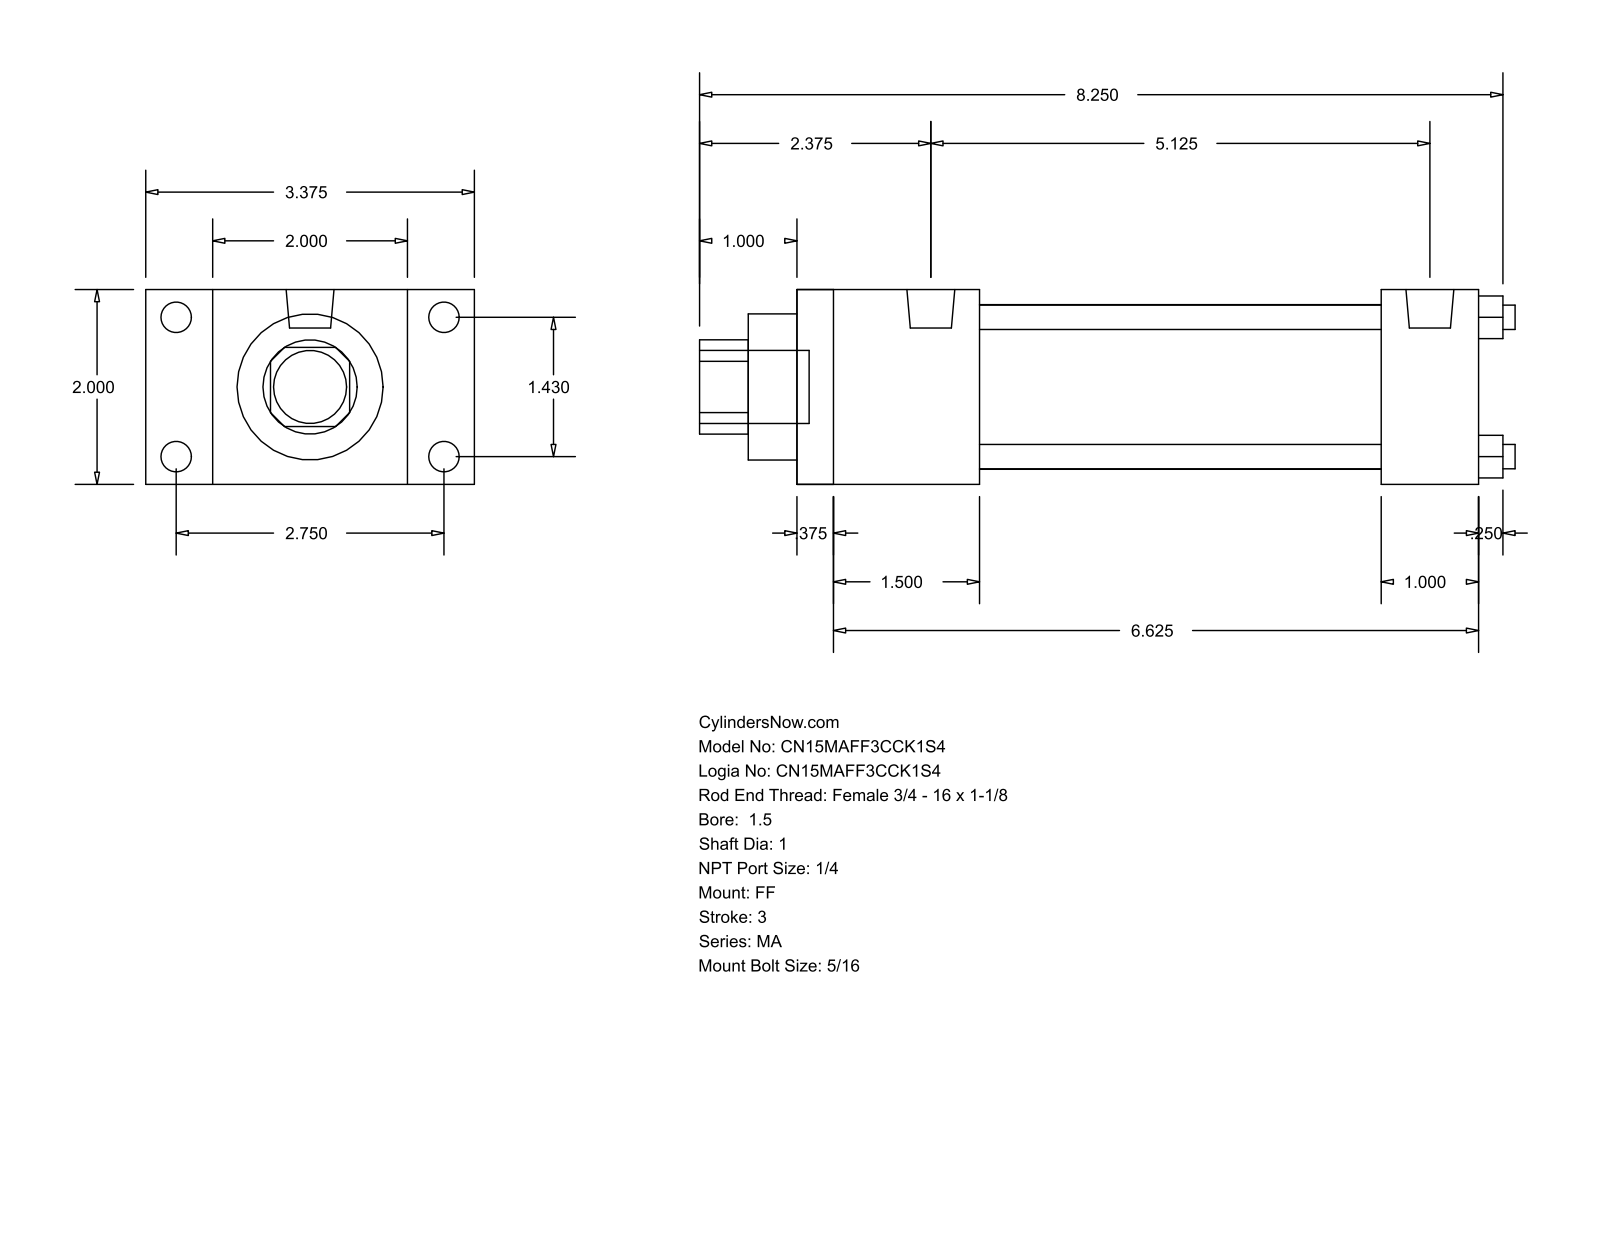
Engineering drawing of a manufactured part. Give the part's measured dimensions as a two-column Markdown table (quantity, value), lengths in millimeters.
| quantity | value |
| --- | --- |
| part name | MA_FF__0150_1 |
| STEP written by | GSSL Pune (CONFIG_CONTROL_DESIGN) |
| units | millimeters |
| bodies | 0 solids, 92 faces (64 planar, 28 cylindrical, 0 other) |
| overall size | 212.72 × 85.72 × 50.8 |
| round holes (diameter × count) | 6.35 × 4, 25.4 × 1, 38.1 × 1, 42.93 × 1 |
| round bosses / shafts (diameter × count) | 7.94 × 8, 12.49 × 2, 19.05 × 1 |
| partial cylindrical surfaces (radius × count) | 12.29 × 1 |
| main face-to-face distances | 50.8, 177.8, 9.52, 168.28, 25.4, 47.63, 152.4, 38.11, 142.88, 104.77 |
| hole center spacings | 25.68, 36.32, 51.36 |
